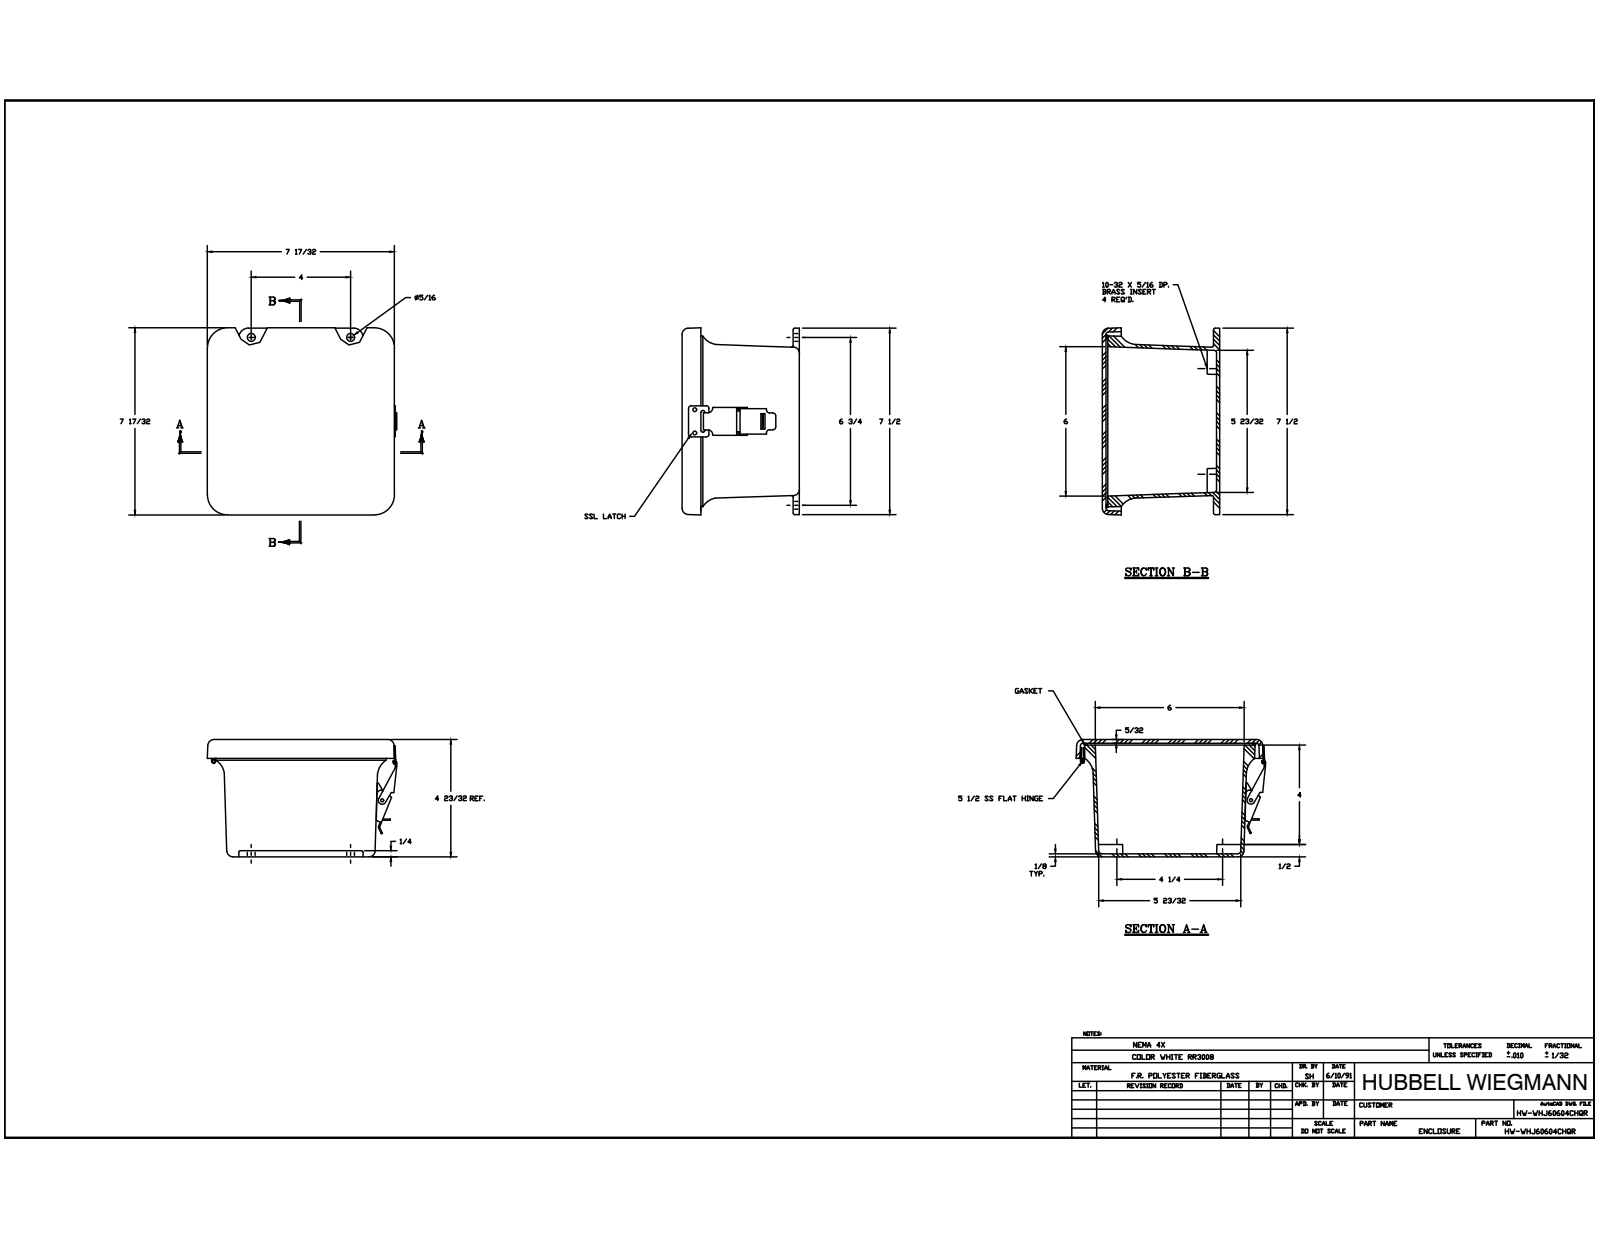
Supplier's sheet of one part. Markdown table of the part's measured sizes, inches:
| quantity | value |
| --- | --- |
| part name | J606HL_7; RMINS45821P_155; RMINS45821P_156; RMINS45821P_157 (+8 more) |
| STEP written by | Autodesk Inventor 2014 (AUTOMOTIVE_DESIGN) |
| units | inches |
| bodies | 25 solids, 631 faces (249 planar, 258 cylindrical, 124 other) |
| overall size | 7.615 × 7.525 × 4.838 |
| volume | 38.1 in³ |
| surface area | 517.3 in² |
| round holes (diameter × count) | 0.14 × 11, 0.131 × 5, 0.152 × 5, 0.104 × 4, 0.156 × 4, 0.218 × 4, 0.13 × 2, 0.135 × 2, 0.085 × 1, 0.375 × 1 |
| round bosses / shafts (diameter × count) | 0.125 × 9, 0.25 × 5, 0.27 × 4, 0.3 × 1, 0.17 × 1, 0.155 × 1, 0.12 × 1 |
| partial cylindrical surfaces (radius × count) | 0.031 × 20, 0.015 × 12, 0.125 × 12, 0.25 × 12, 0.045 × 8, 0.03 × 6, 0.022 × 5, 0.06 × 4 |
| main face-to-face distances | 0.147, 4.691, 4.838, 0.125, 4.566, 4.713, 0.152, 4.5, 0.066, 4.625 |
| hole center spacings | 5.308, 0.937, 1.37, 2.5, 4.25, 6.187, 7.38, 0.75 |
